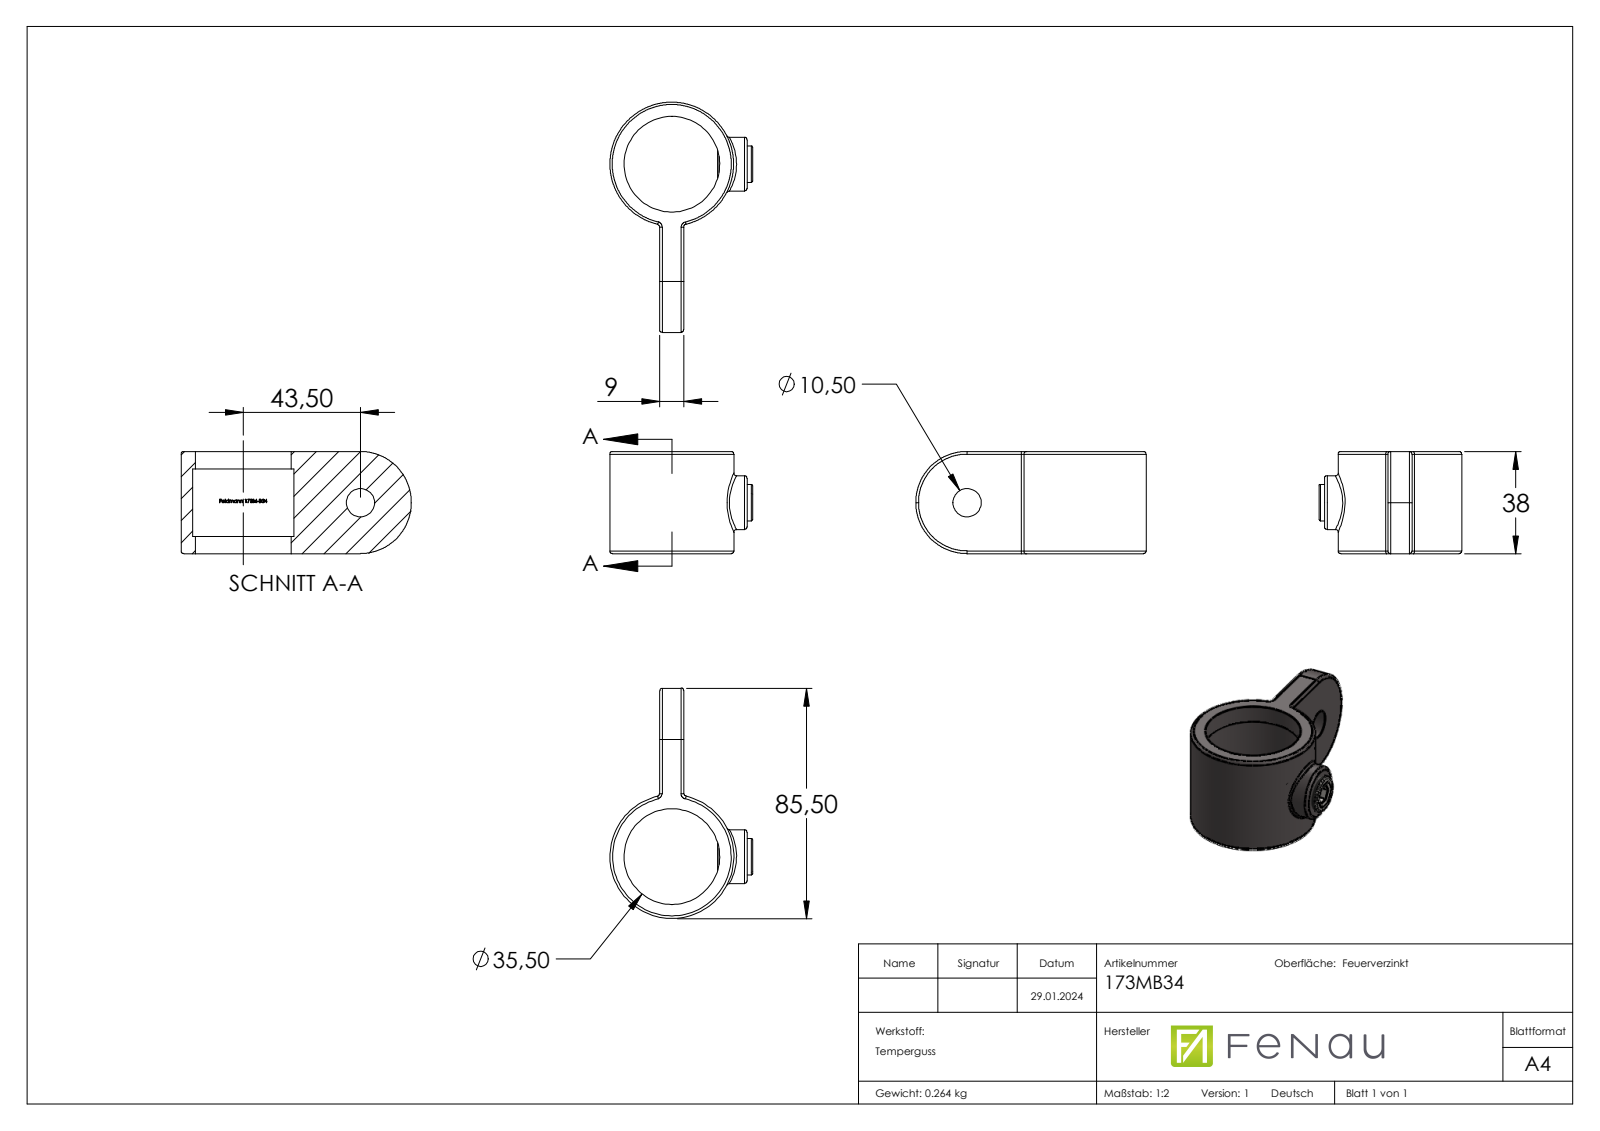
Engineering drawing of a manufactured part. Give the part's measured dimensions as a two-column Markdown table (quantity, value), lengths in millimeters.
| quantity | value |
| --- | --- |
| part name | 173M-B34; 173M-B34 Teil 1_173M-B34 Teil 1; 173M-B34 Teil 2_173M-B34 Teil 2 |
| STEP written by | SolidWorks 2018 (CONFIG_CONTROL_DESIGN) |
| units | millimeters |
| bodies | 2 solids, 275 faces (126 planar, 50 cylindrical, 99 other) |
| overall size | 85.5 × 53 × 38 |
| volume | 36 060 mm³ |
| surface area | 16 155 mm² |
| round holes (diameter × count) | 10.5 × 1, 11.8 × 1, 35.5 × 1, 37.5 × 1 |
| round bosses / shafts (diameter × count) | 46 × 1, 20 × 1, 13.5 × 1 |
| partial cylindrical surfaces (radius × count) | 2 × 12, 1 × 6, 18.85 × 1, 19 × 1 |
| main face-to-face distances | 9, 38, 6.5, 31.5, 32.5, 23.5, 6.4, 25, 15.8, 22.2 |
| hole center spacings | 43.5 |
